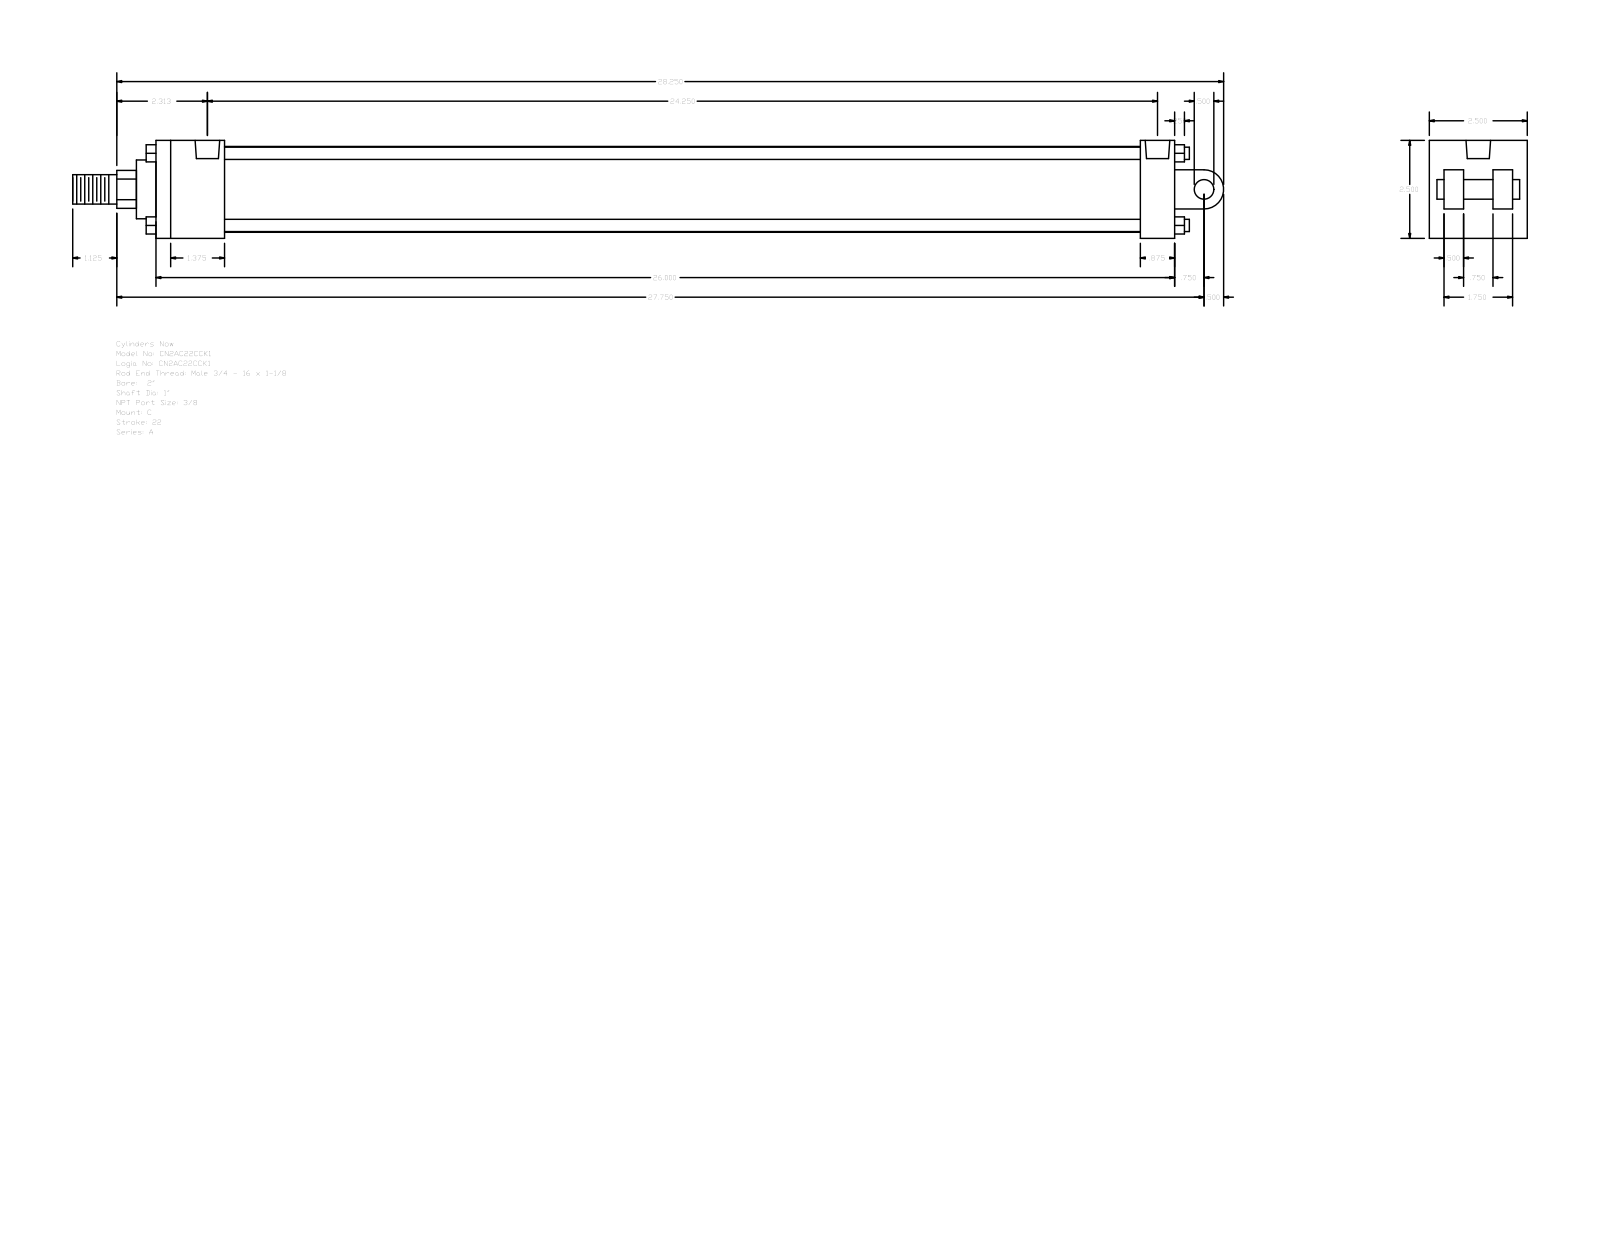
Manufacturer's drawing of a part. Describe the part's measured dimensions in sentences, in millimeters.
The part is named "A_C__0200_1". Its 3-D file was written by "GSSL Pune (CONFIG_CONTROL_DESIGN)". It is 0 solids with 135 faces: 102 planar, 33 cylindrical and 0 other. Overall it measures 746.12 by 63.5 by 63.5 millimeters. Round holes: 4 of diameter 5.56, 2 of diameter 15.93. Round bosses or shafts: 4 of diameter 7.94, 1 of diameter 55.63, 1 of diameter 38.1, 1 of diameter 25.4, 1 of diameter 19.05, 1 of diameter 12.7. Partial cylindrical surfaces (rounded edges, fillets, slot ends): 1 of radius 12.29, 1 of radius 12.7. The main face-to-face distances are 63.5, 22.22, 660.4, 44.45, 12.7, 615.95, 638.18, 593.73, 9.52, 53.98. The hole center spacings are 610.38, 1.59, 3.98, 611.97, 614.36, 615.95.
